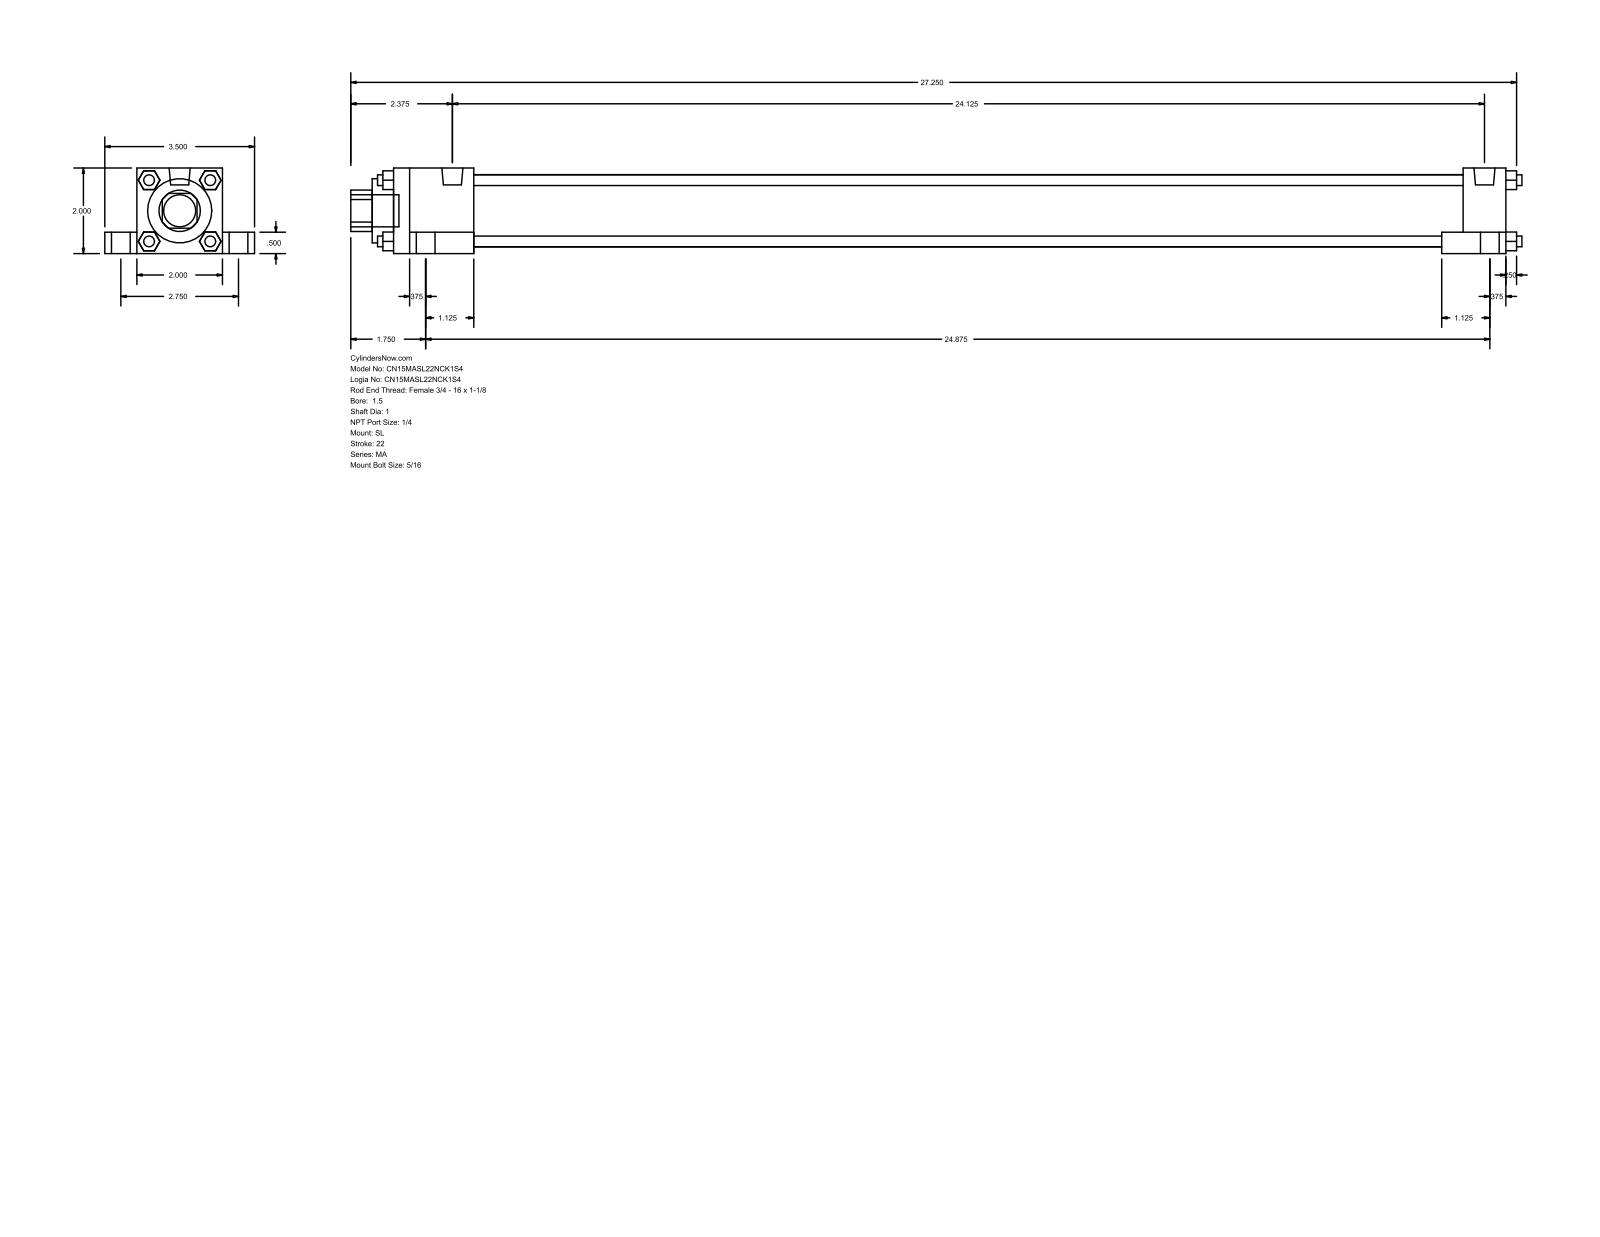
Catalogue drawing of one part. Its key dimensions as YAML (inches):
part_name: "MA_SL__0150_1"
step_written_by: "GSSL Pune (CONFIG_CONTROL_DESIGN)"
units: inches
bodies: {solids: 0, faces: 148, planar: 112, cylindrical: 36, other: 0}
overall_size: [27.375, 3.5, 2]
round_holes:
  - {diameter: 1, count: 1}
  - {diameter: 1.5, count: 1}
  - {diameter: 1.69, count: 1}
round_bosses_or_shafts:
  - {diameter: 0.687, count: 4}
  - {diameter: 0.437, count: 4}
  - {diameter: 0.313, count: 4}
  - {diameter: 0.25, count: 4}
  - {diameter: 0.492, count: 2}
  - {diameter: 0.75, count: 1}
partial_cylinders:
  - {radius: 0.484, count: 1}
face_to_face_distances: [2, 0.5, 0.75, 2.75, 0.375, 1.5, 0.25, 26, 1, 25]
